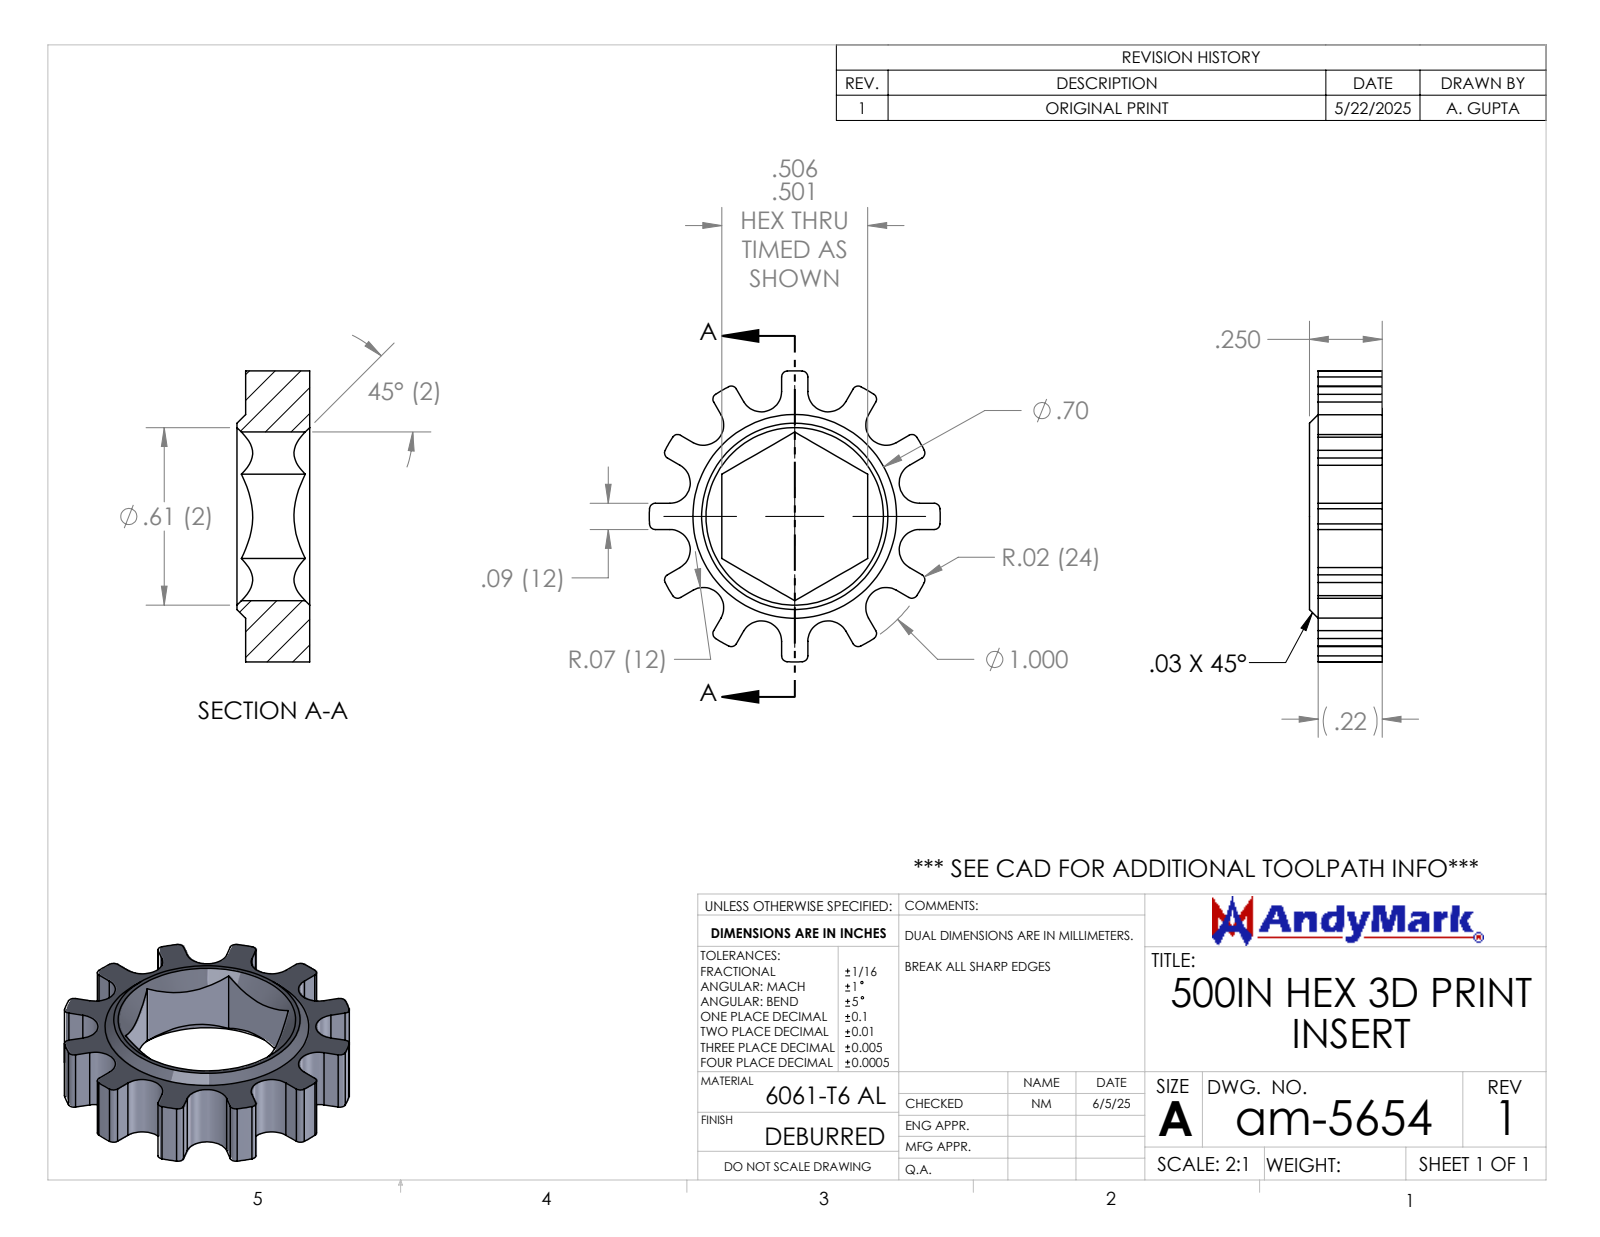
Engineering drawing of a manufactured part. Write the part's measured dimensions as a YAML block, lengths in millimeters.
part_name: "am-5654 500in Hex 3D Print Insert"
step_written_by: "SolidWorks 2024 (AUTOMOTIVE_DESIGN)"
units: millimeters
bodies: {solids: 1, faces: 96, planar: 33, cylindrical: 57, other: 6}
overall_size: [25.4, 25.4, 6.4]
volume: 1300
surface_area: 1399
partial_cylinders:
  - {radius: 0.5, count: 24}
  - {radius: 1.8, count: 12}
  - {radius: 12.7, count: 1}
face_to_face_distances: [5.6, 12.8, 5.2, 7.5, 2.3, 6.4, 0.8]
